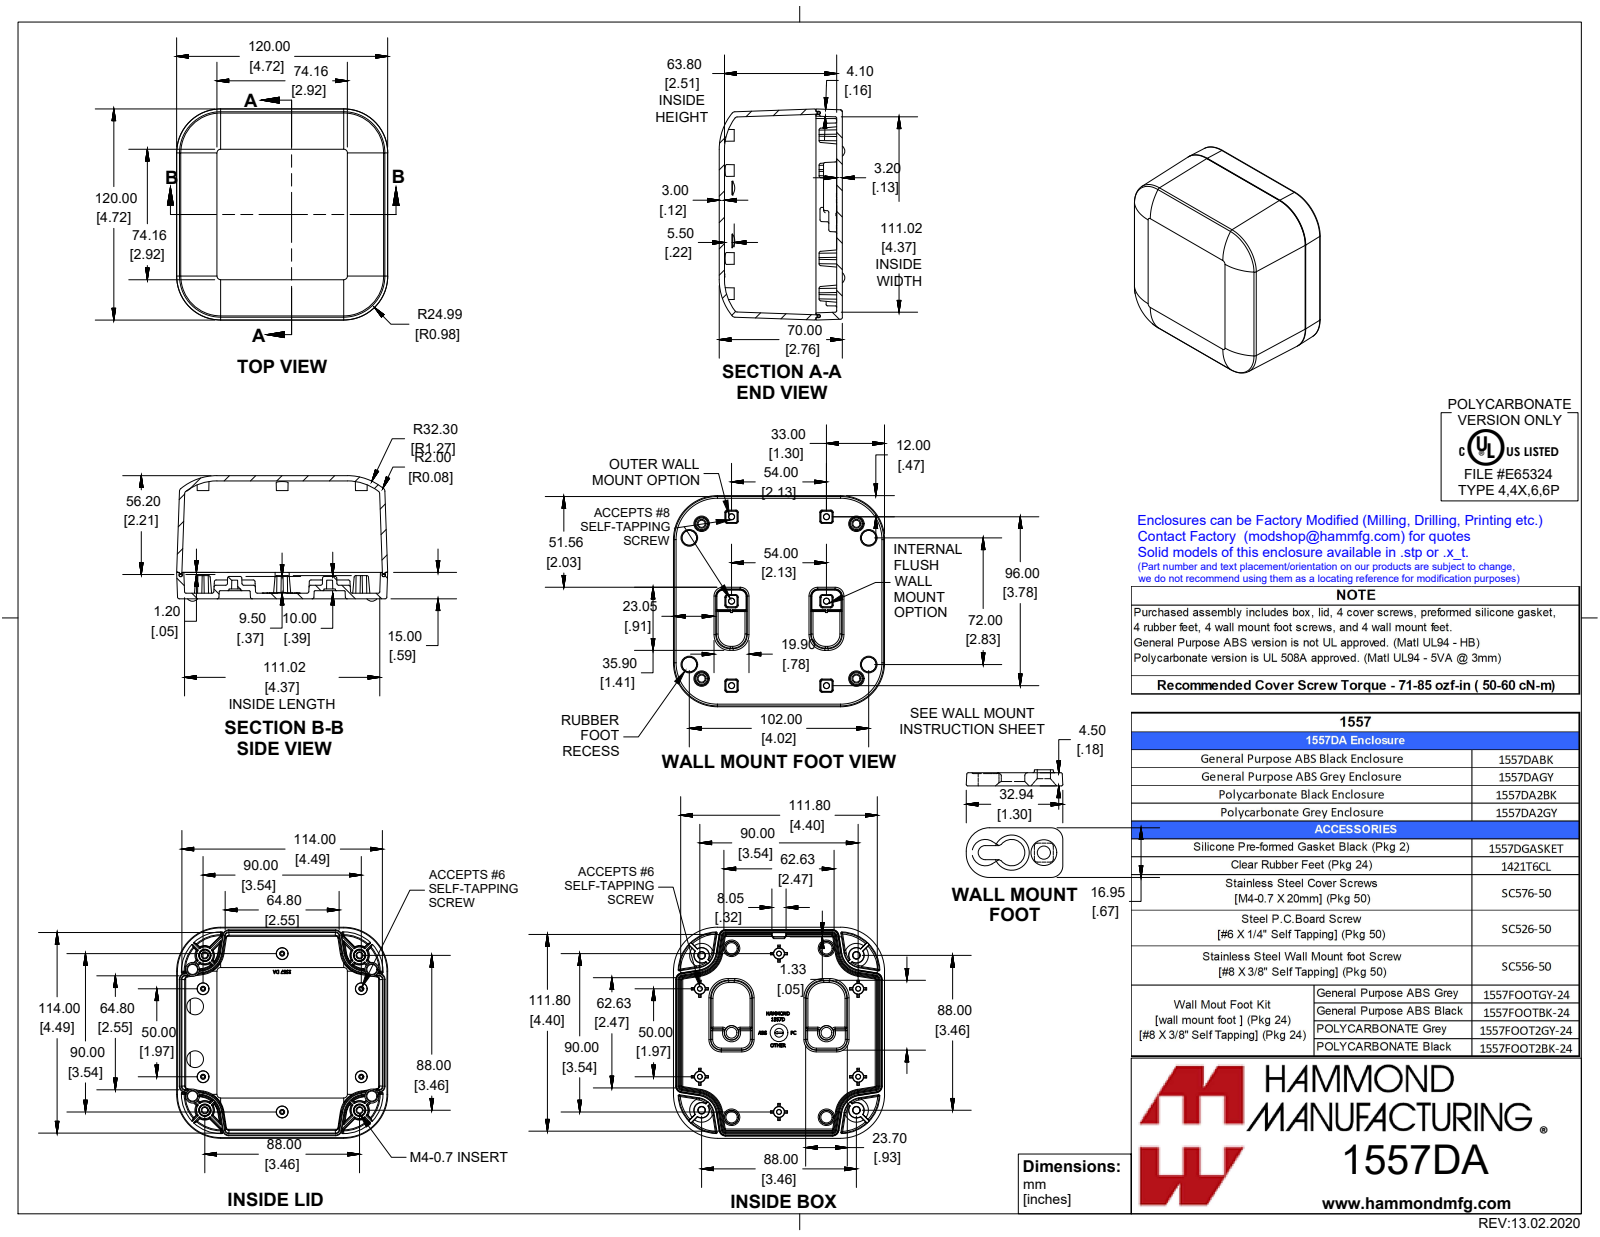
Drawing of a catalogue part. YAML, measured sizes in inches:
part_name: "1557FA TOP; 1557H Gaskets; PFR1421T4; (screw #8X 3_8''''''''FH Self-tap plastite) (+5 more)"
step_written_by: "SolidWorks 2019 (CONFIG_CONTROL_DESIGN)"
units: inches
bodies: {solids: 23, faces: 2880, planar: 936, cylindrical: 567, other: 1377}
overall_size: [5.864, 4.724, 2.933]
volume: 13.47
surface_area: 247
round_holes:
  - {diameter: 0.128, count: 4}
  - {diameter: 0.177, count: 4}
round_bosses_or_shafts:
  - {diameter: 0.071, count: 12}
  - {diameter: 0.313, count: 4}
  - {diameter: 0.303, count: 4}
  - {diameter: 0.25, count: 4}
  - {diameter: 0.218, count: 4}
  - {diameter: 0.21, count: 4}
  - {diameter: 0.165, count: 4}
  - {diameter: 0.153, count: 4}
partial_cylinders:
  - {radius: 0.02, count: 101}
  - {radius: 0.039, count: 79}
  - {radius: 0.157, count: 12}
  - {radius: 0.008, count: 8}
  - {radius: 0.012, count: 8}
  - {radius: 0.016, count: 8}
  - {radius: 0.059, count: 8}
  - {radius: 0.083, count: 8}
face_to_face_distances: [0.118, 0.126, 0.118, 2.756, 2.638, 2.512, 2.63, 4.602, 4.72, 3.27]
hole_center_spacings: [0.687, 2.8, 3.465, 3.683, 4.575, 2.126, 3.78, 4.337]
